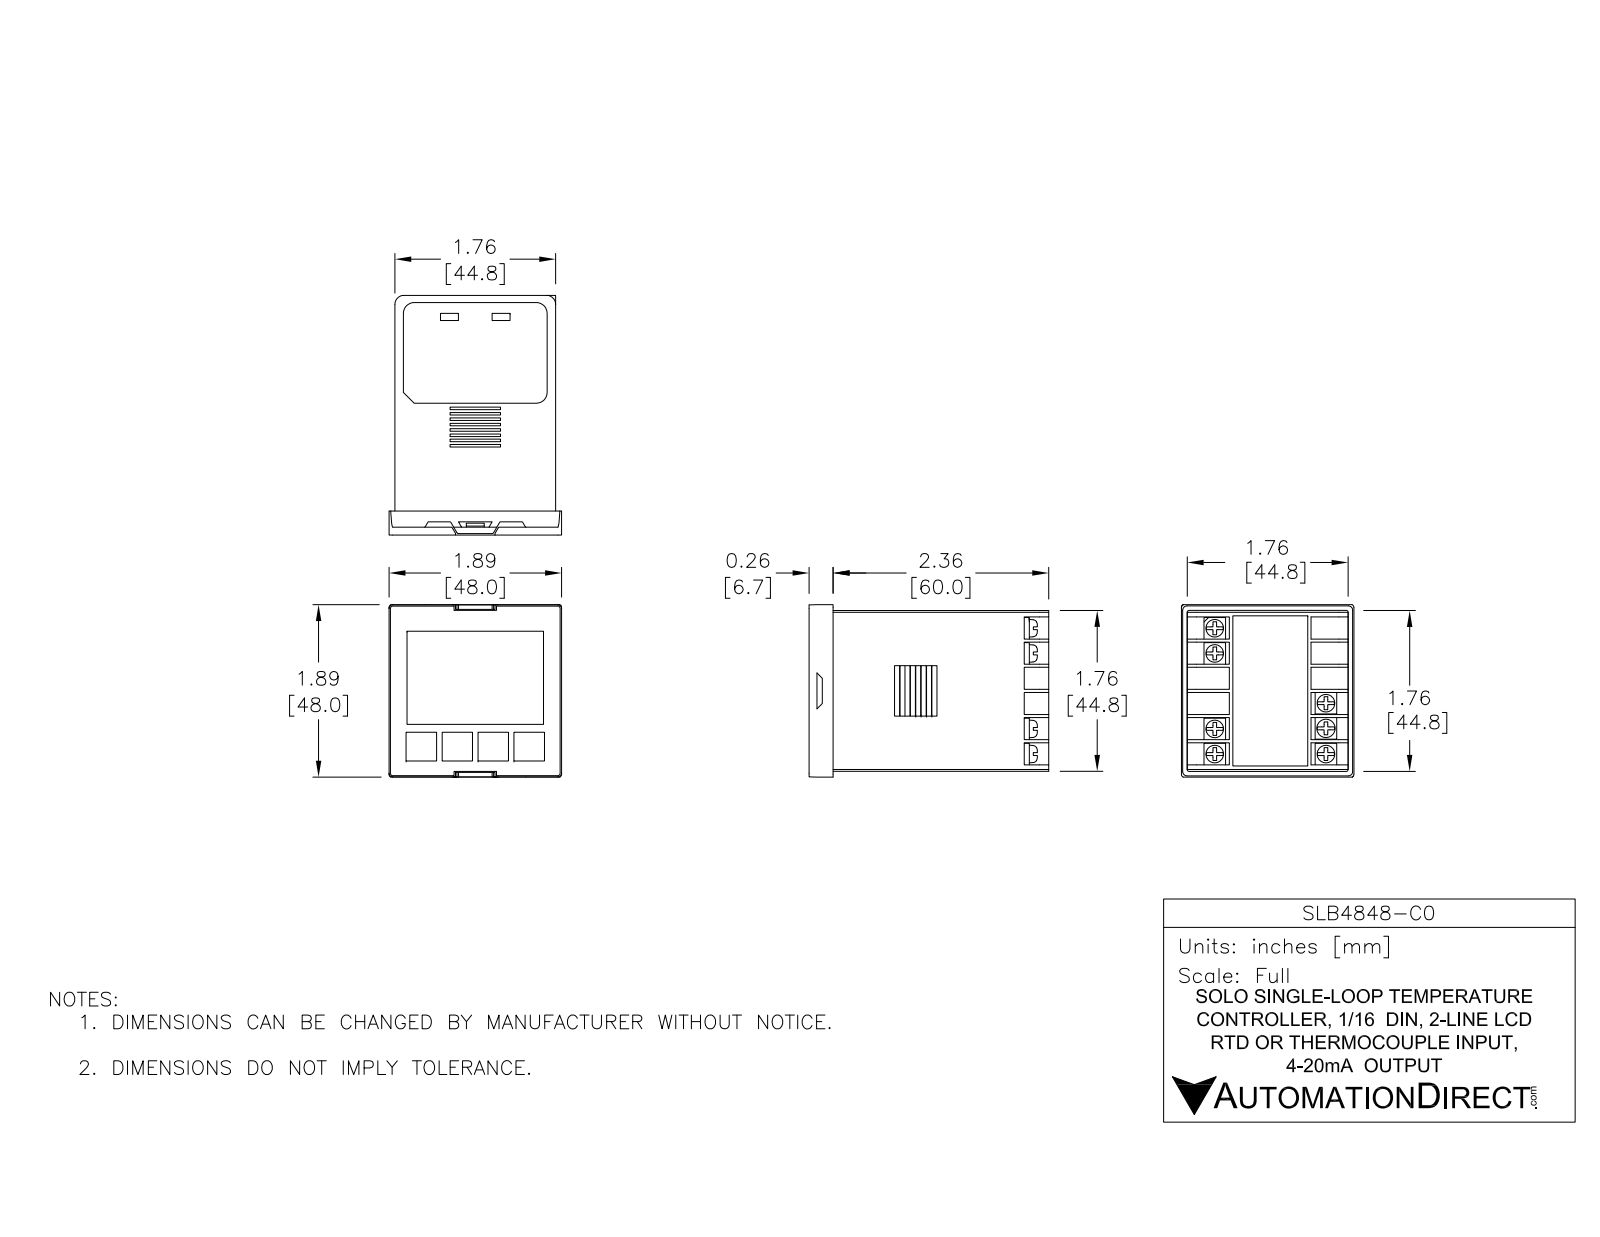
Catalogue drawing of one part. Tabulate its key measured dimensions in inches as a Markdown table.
| quantity | value |
| --- | --- |
| part name | SLB4848-C0 |
| STEP written by | SolidWorks 2017 (AUTOMOTIVE_DESIGN) |
| units | inches |
| bodies | 5 solids, 3364 faces (3117 planar, 141 cylindrical, 106 other) |
| overall size | 2.628 × 2.234 × 1.89 |
| volume | 7.68 in³ |
| surface area | 46.55 in² |
| round bosses / shafts (diameter × count) | 0.21 × 2, 0.114 × 2 |
| partial cylindrical surfaces (radius × count) | 0.006 × 36, 0.008 × 8, 0.02 × 6, 0.039 × 6, 0.024 × 4, 0.04 × 4, 0.063 × 4, 0.157 × 4 |
| main face-to-face distances | 1.762, 0.049, 1.813, 0.016, 1.746, 0.05, 1.763, 1.764, 1.763, 1.812 |
